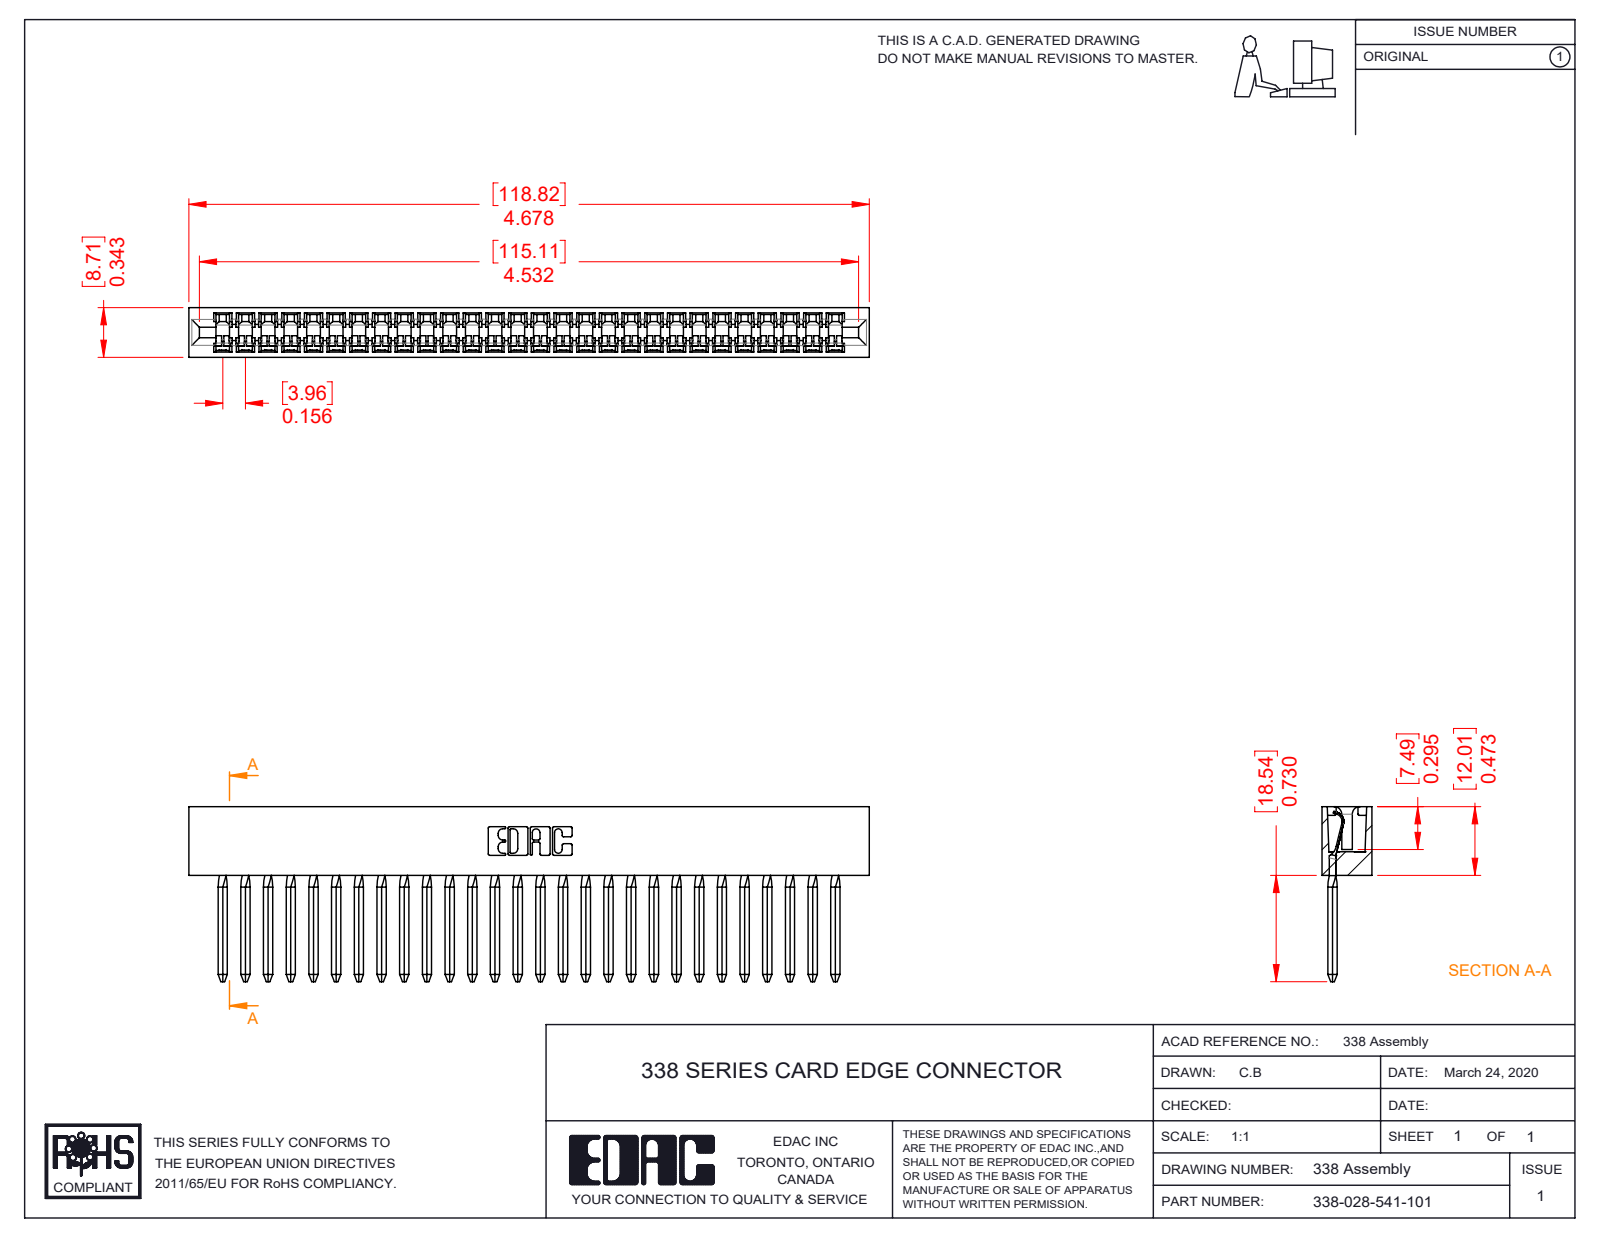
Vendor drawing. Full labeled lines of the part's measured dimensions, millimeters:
Part name (STEP PRODUCT): 338-028-541-101; 338-290-001_541; 338-210-001_338-210-028-001
STEP written by: SolidWorks 2016 (CONFIG_CONTROL_DESIGN)
Units: millimetres
Bodies: 29 solids, 2690 faces (1866 planar, 712 cylindrical, 112 other)
Overall size (bounding box): 118.8 × 30.6 × 8.7
Volume: 8 640 mm³ · Surface area: 14 530 mm²
Partial cylindrical surfaces — rounded edges, fillets, slot ends (radius × count): R0.6 ×114, R0.2 ×28, R1.4 ×23, R1.7 ×23, R0.3 ×22, R2.5 ×22, R0.2 ×6, R0.8 ×6
Main face-to-face distances: 8.7, 4, 15.8, 2.8, 5.3, 3.4, 19.8, 11.9, 1.2, 31.7
